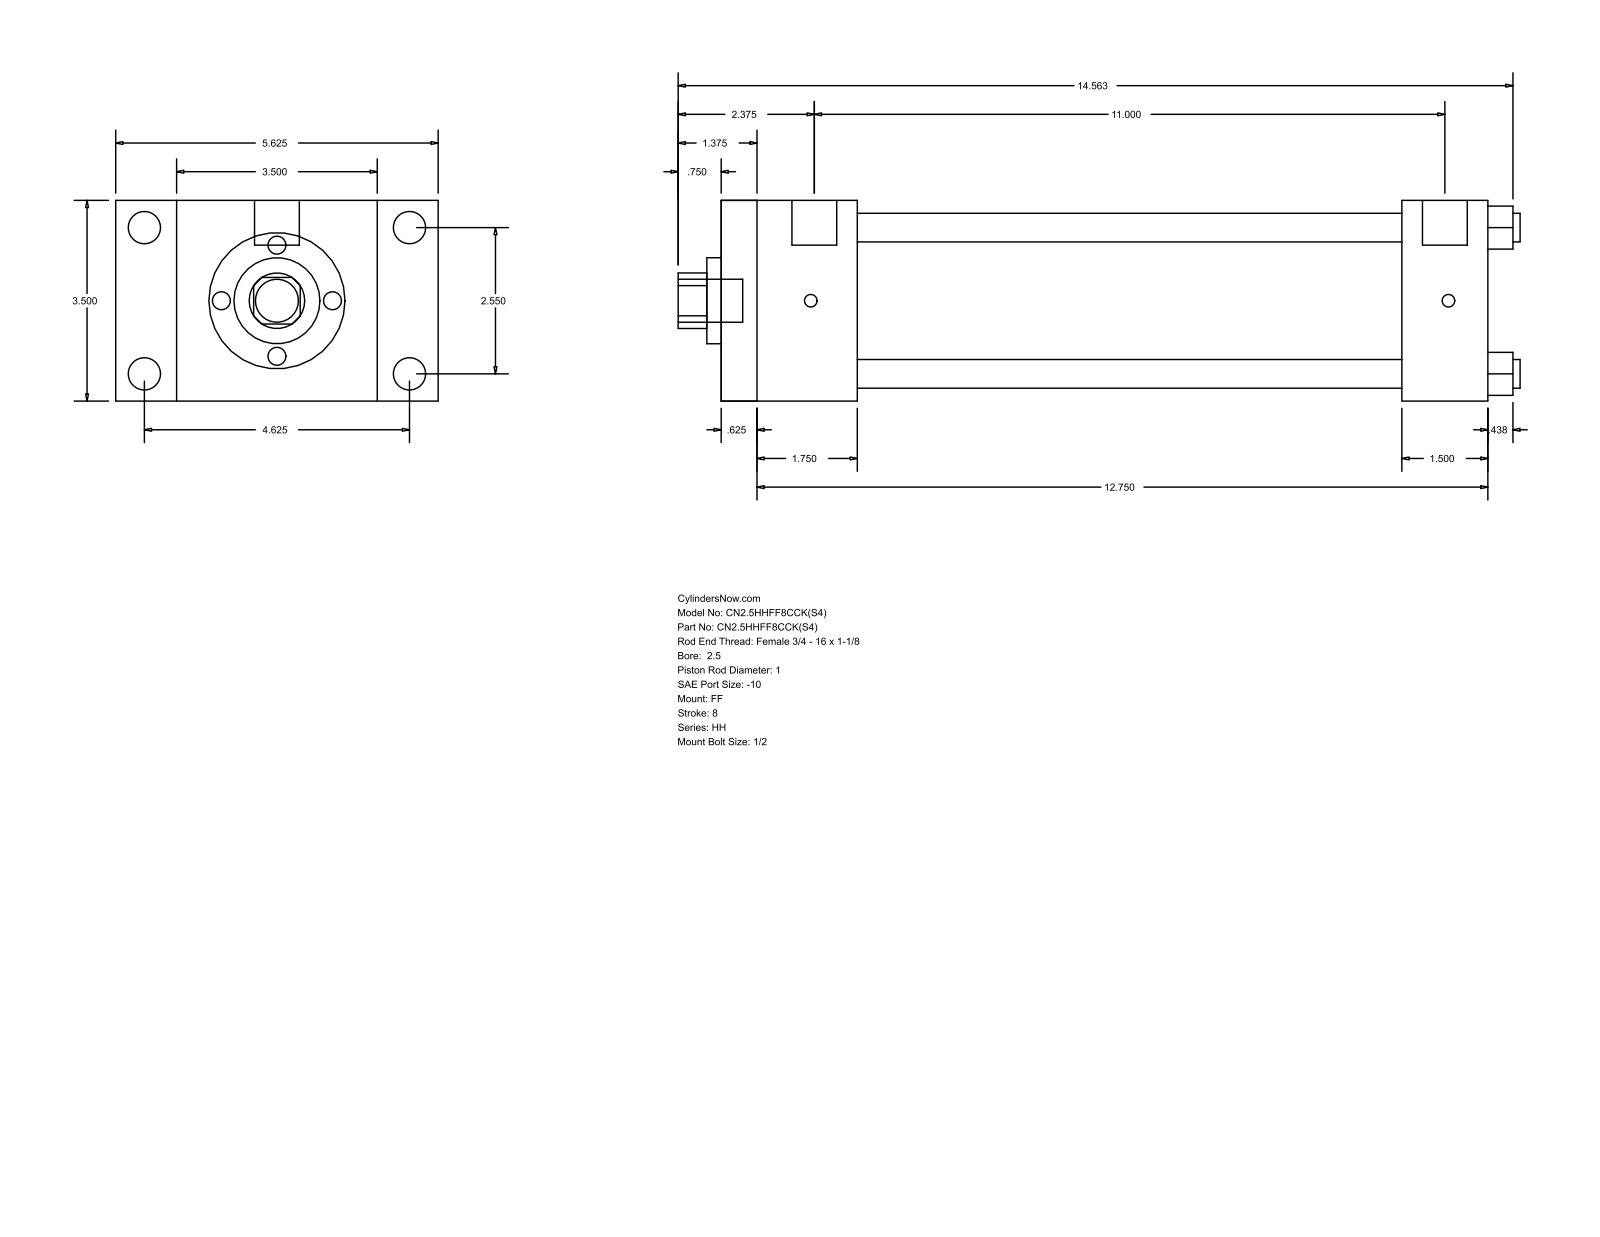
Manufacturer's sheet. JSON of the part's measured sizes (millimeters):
{"part_name": "HH_FF__0250_1", "step_written_by": "GSSL Pune (CONFIG_CONTROL_DESIGN)", "units": "millimeters", "bodies": {"solids": 0, "faces": 92, "planar": 64, "cylindrical": 28, "other": 0}, "overall_size": [373.06, 142.88, 88.9], "round_holes": [[12.7, 4], [25.4, 1], [38.1, 1], [73.03, 1]], "round_bosses_or_shafts": [[14.3, 4], [5.56, 4], [19.84, 2], [19.05, 1]], "partial_cylinders_radius": [[12.29, 1]], "face_to_face_distances": [88.9, 339.72, 15.87, 323.85, 60.33, 44.46, 279.39, 301.63, 285.76, 241.3], "hole_center_spacings": [45.79, 64.76, 91.58]}
